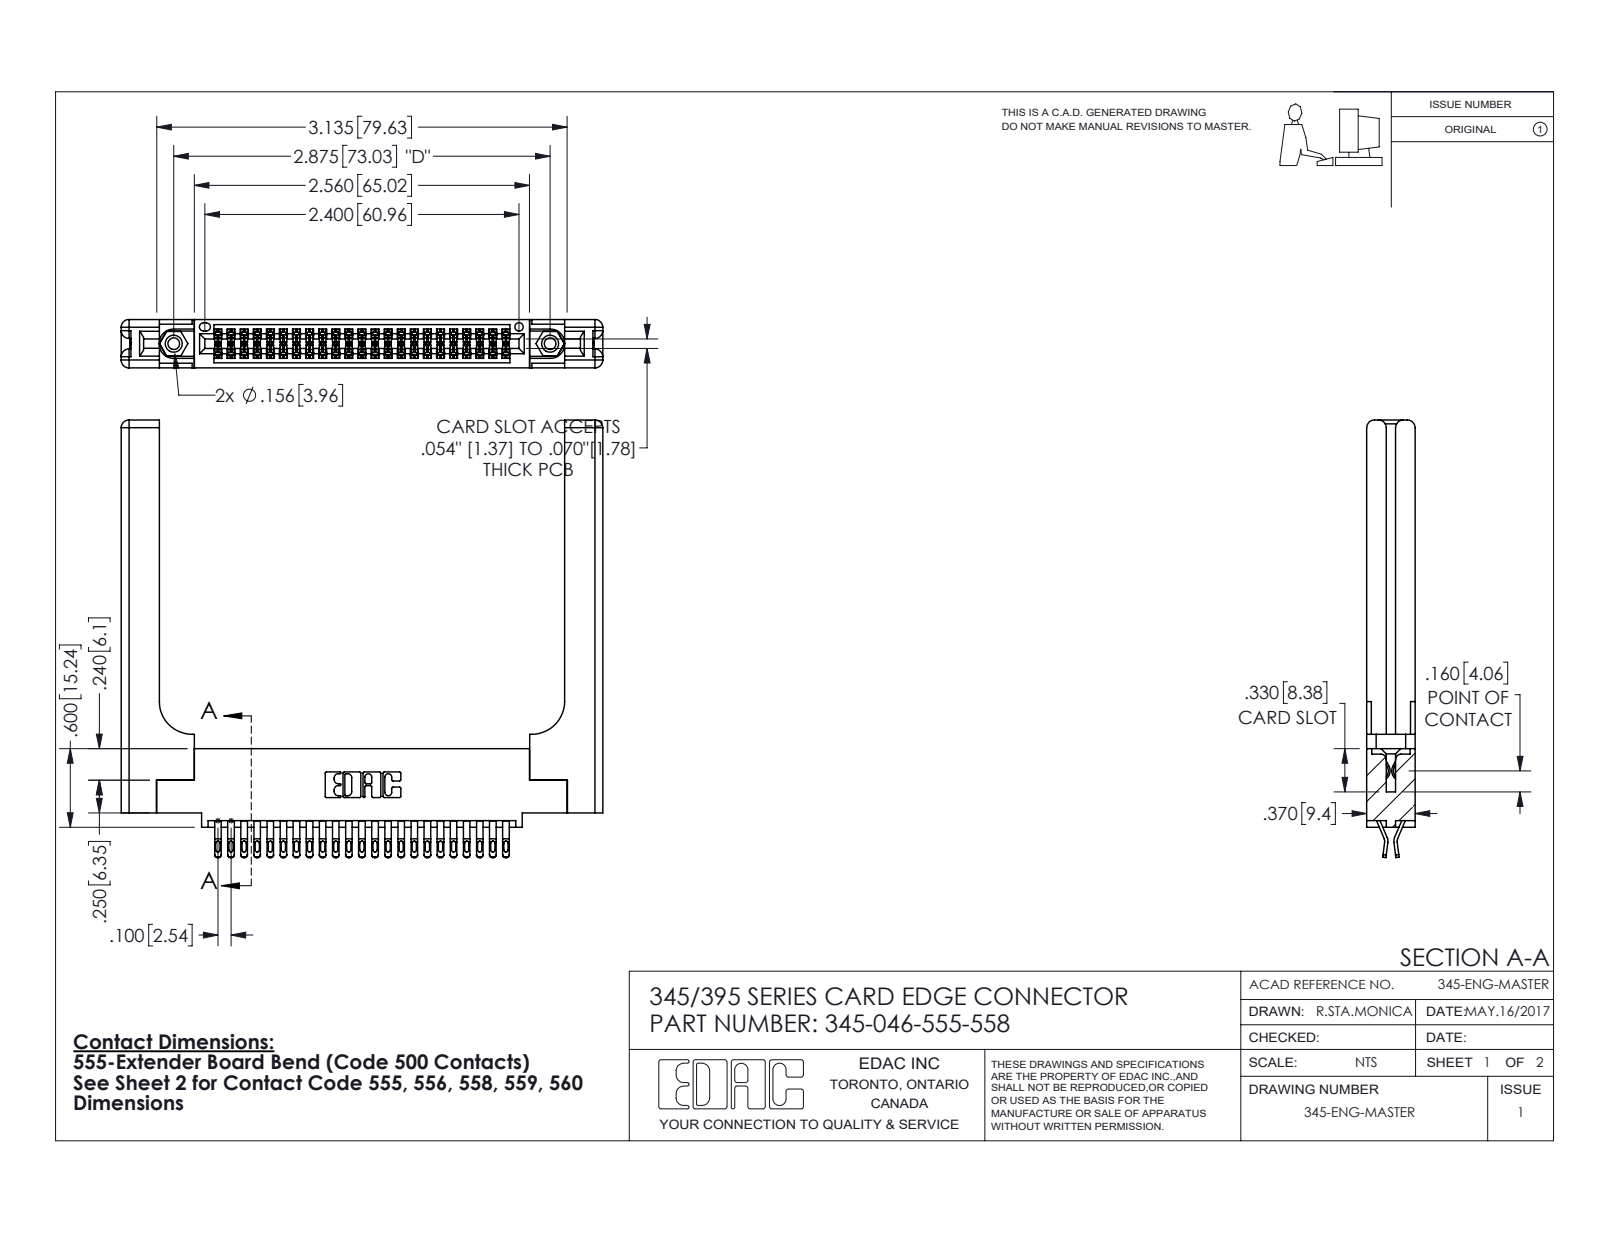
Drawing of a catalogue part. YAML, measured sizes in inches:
part_name: "345-220-058_345-220-058; 345-046-555-558; 345-292-001_555 Tail; 345 Part_0.110 Offset - 0.156 Dia-TH (+1 more)"
step_written_by: "SolidWorks 2016 (CONFIG_CONTROL_DESIGN)"
units: inches
bodies: {solids: 51, faces: 2962, planar: 1658, cylindrical: 1244, other: 60}
overall_size: [3.679, 3.342, 0.37]
volume: 1.064
surface_area: 28.67
round_holes:
  - {diameter: 0.089, count: 2}
  - {diameter: 0.125, count: 2}
  - {diameter: 0.156, count: 2}
  - {diameter: 0.064, count: 1}
round_bosses_or_shafts:
  - {diameter: 0.155, count: 2}
partial_cylinders:
  - {radius: 0.016, count: 115}
  - {radius: 0.02, count: 92}
  - {radius: 0.006, count: 69}
  - {radius: 0.01, count: 22}
  - {radius: 0.06, count: 16}
  - {radius: 0.007, count: 6}
  - {radius: 0.031, count: 6}
  - {radius: 0.026, count: 3}
face_to_face_distances: [0.37, 0.072, 0.298, 0.025, 0.15, 0.148, 0.077, 0.225, 0.098, 0.272]
hole_center_spacings: [0.27, 2.641, 2.875]
